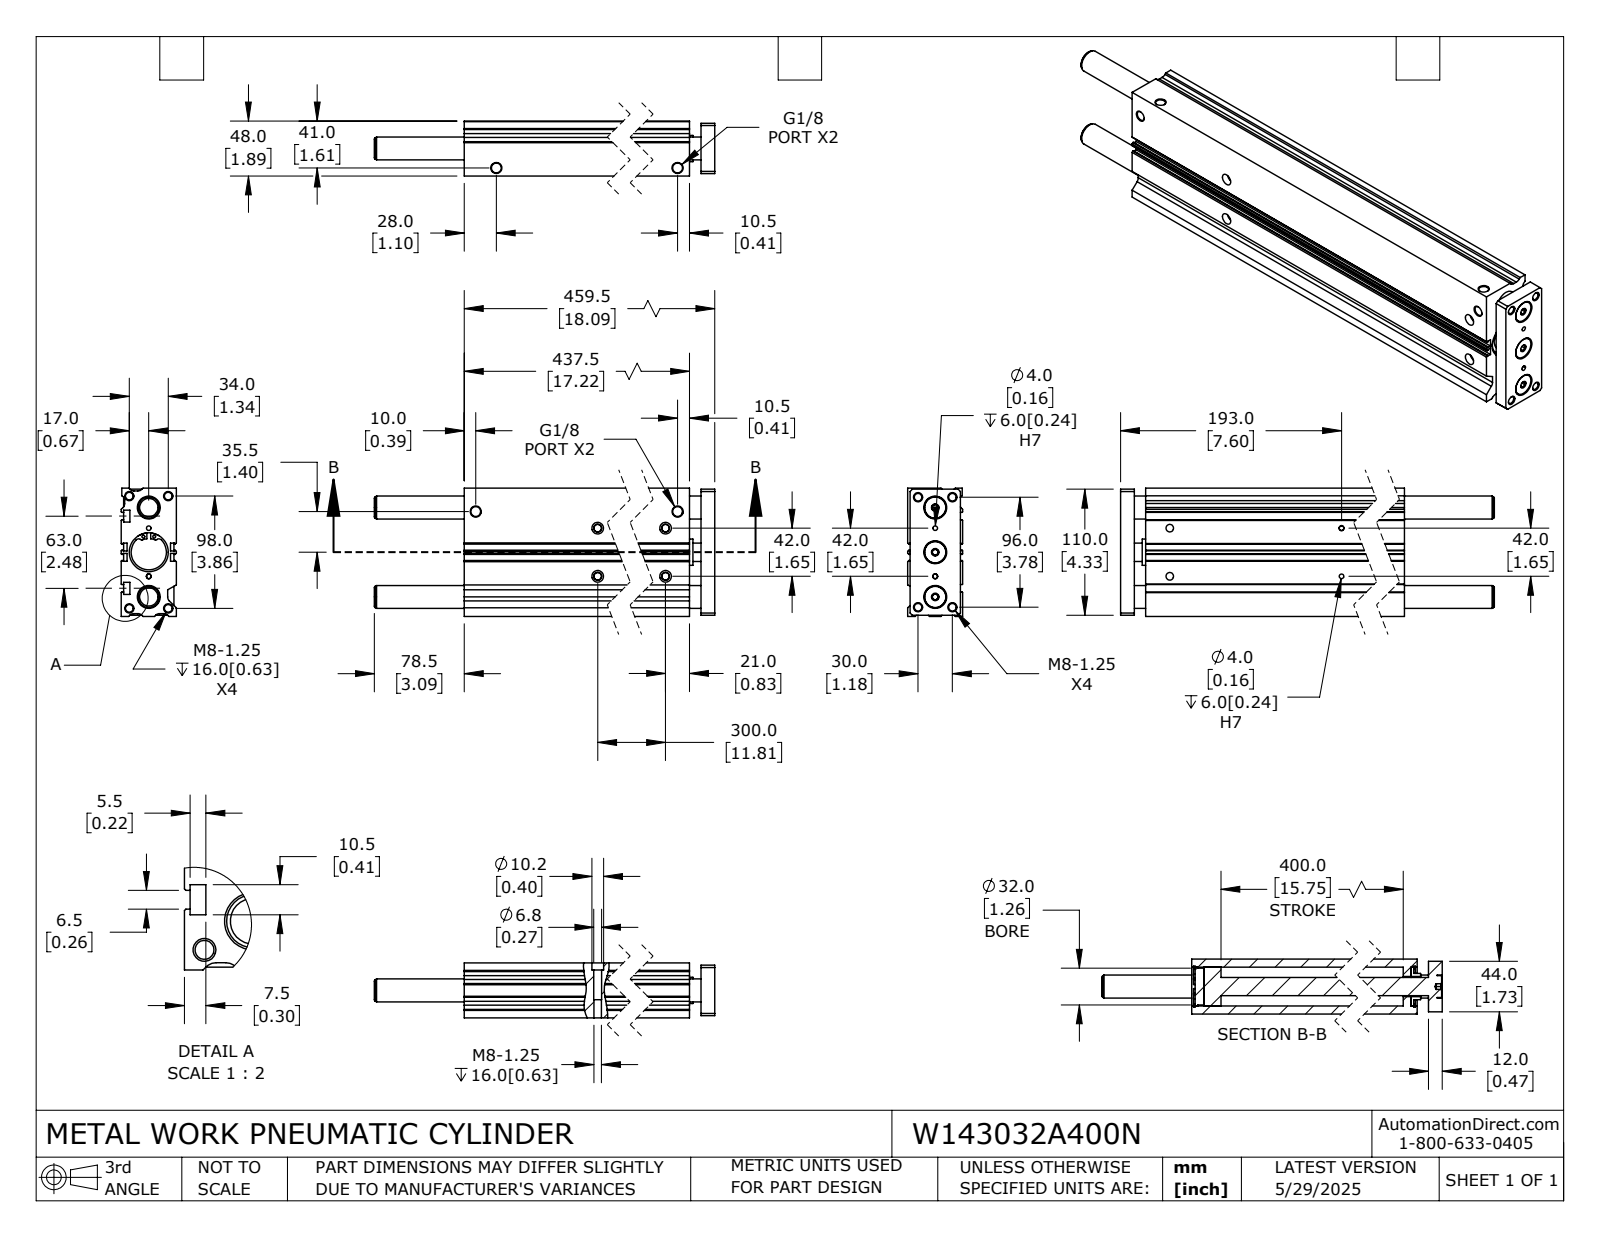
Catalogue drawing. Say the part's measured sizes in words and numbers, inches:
The part is named "W143032A400N; W143032A400N_ROD; W143032A400N_BODY". Its 3-D file was written by "SolidWorks 2024 (CONFIG_CONTROL_DESIGN)". It is 6 solids with 394 faces: 195 planar, 149 cylindrical and 50 other. Overall it measures 21.181 by 4.409 by 1.89 inches. Its volume is 119.4 cubic inches and its surface area 644 square inches. Round holes: 10 of diameter 0.262, 4 of diameter 0.098, 4 of diameter 0.157, 4 of diameter 0.268, 4 of diameter 0.337, 4 of diameter 0.402, 3 of diameter 0.197, 3 of diameter 0.787, 2 of diameter 0.262, 1 of diameter 0.697, 1 of diameter 1.211. Round bosses or shafts: 3 of diameter 0.748, 2 of diameter 1.406, 1 of diameter 1.339, 1 of diameter 1.26, 1 of diameter 0.906, 1 of diameter 0.63. Partial cylindrical surfaces (rounded edges, fillets, slot ends): 9 of radius 0.197, 4 of radius 0.079, 4 of radius 0.118, 2 of radius 0.507. The main face-to-face distances are 1.89, 0.098, 0.295, 1.693, 0.197, 1.594, 4.409, 0.079, 0.118, 1.398. The hole center spacings are 0.088, 0.348, 0.566, 0.689, 0.776, 1.019, 1.216, 1.261.
